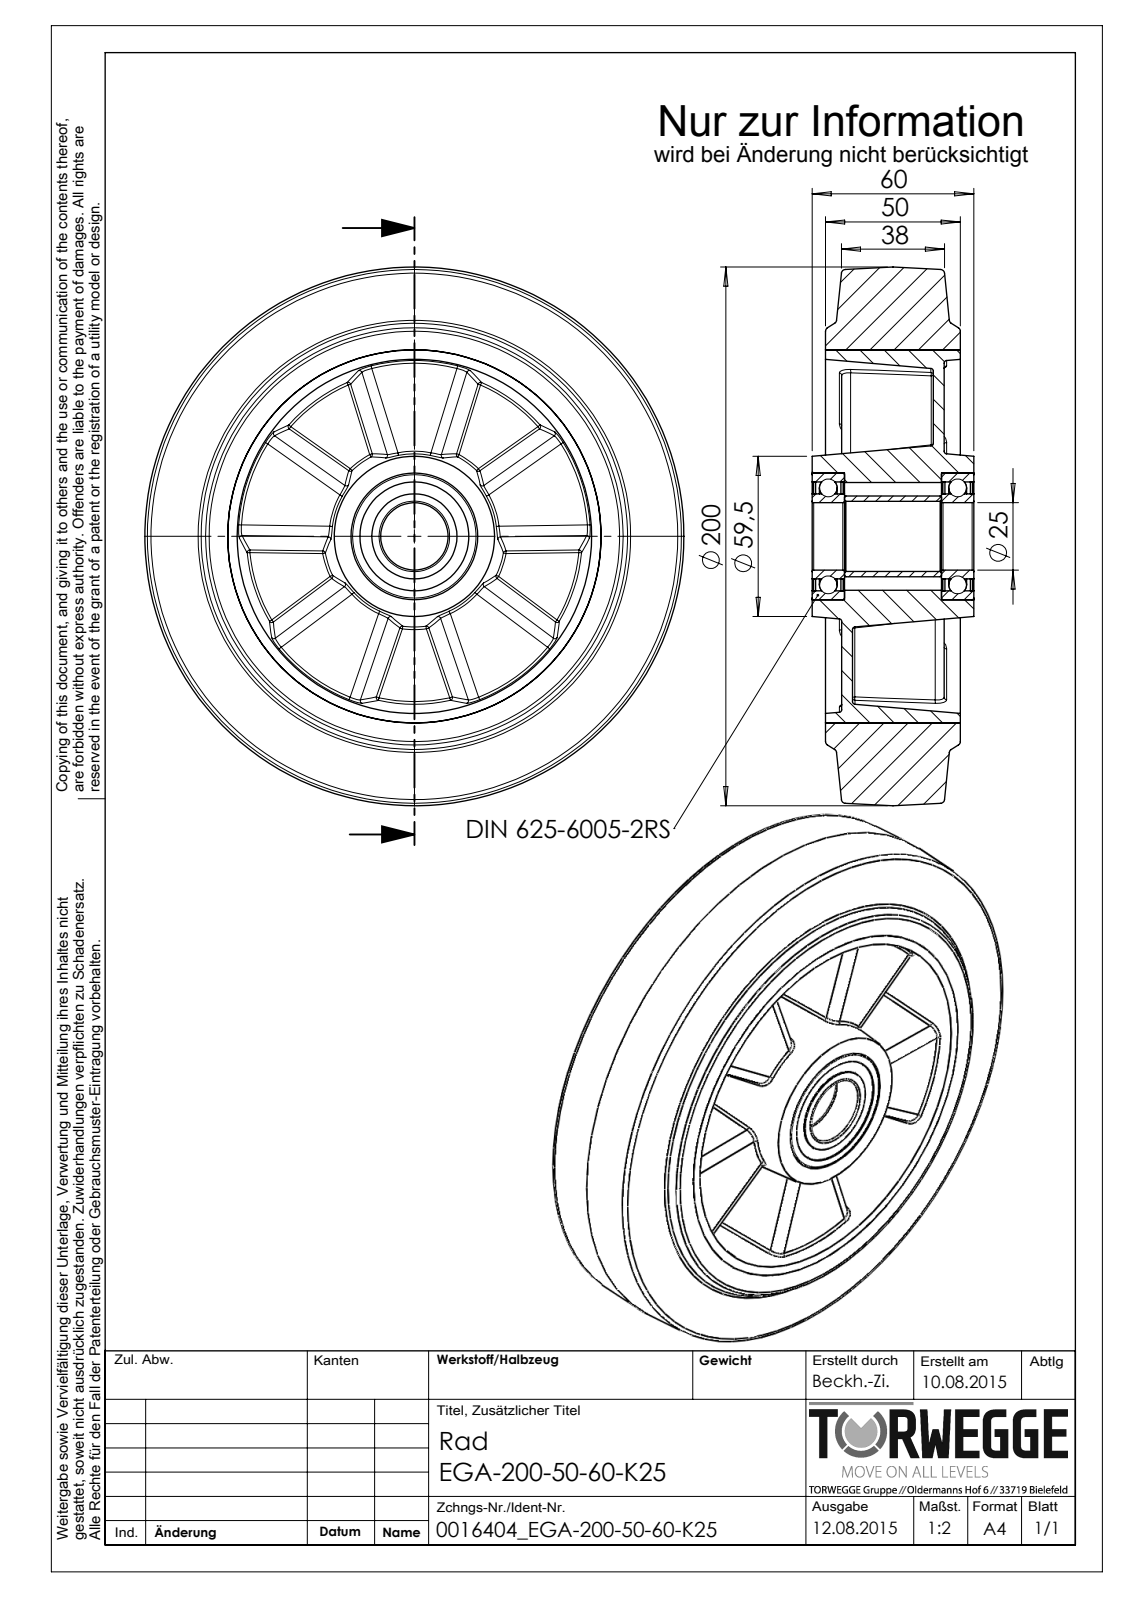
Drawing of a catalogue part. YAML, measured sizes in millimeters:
part_name: "0016404_EGA-200-50-60-K25"
step_written_by: "SolidWorks 2016 (AUTOMOTIVE_DESIGN)"
units: millimeters
bodies: {solids: 9, faces: 404, planar: 66, cylindrical: 94, other: 244}
overall_size: [200, 200, 60]
volume: 1006000
surface_area: 201313
round_holes:
  - {diameter: 25, count: 1}
  - {diameter: 26, count: 1}
  - {diameter: 31.6, count: 1}
  - {diameter: 40, count: 1}
  - {diameter: 40.4, count: 1}
  - {diameter: 47, count: 1}
  - {diameter: 138.5, count: 1}
round_bosses_or_shafts:
  - {diameter: 30, count: 1}
partial_cylinders:
  - {radius: 1, count: 20}
  - {radius: 4, count: 20}
face_to_face_distances: [6, 44, 6.61, 10, 40, 4, 34, 50, 48, 11]
